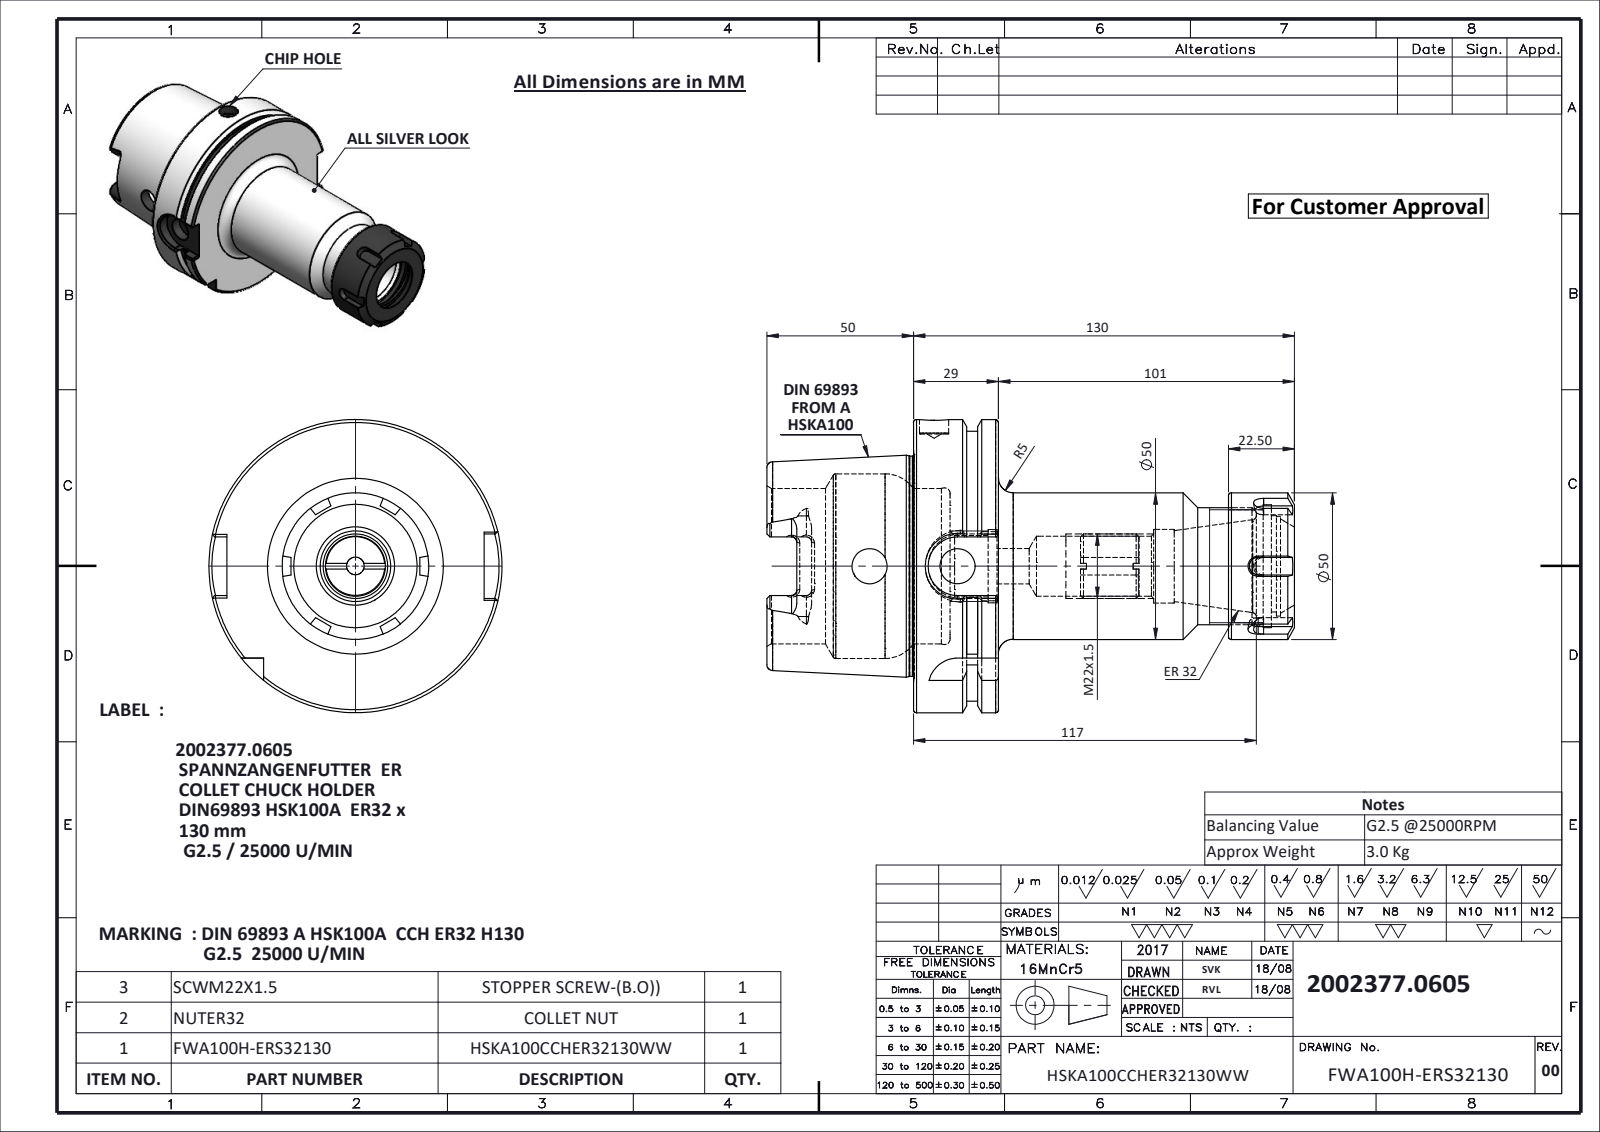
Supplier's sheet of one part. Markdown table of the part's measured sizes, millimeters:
| quantity | value |
| --- | --- |
| part name | FTNUTER32; FWA100H-ERS32130; FTSCWM22X1.5; HSKA100CCHER32130WW |
| STEP written by | SolidWorks 2024 (CONFIG_CONTROL_DESIGN) |
| units | millimeters |
| bodies | 3 solids, 259 faces (95 planar, 68 cylindrical, 96 other) |
| overall size | 180 × 100 × 100 |
| volume | 400 934 mm³ |
| surface area | 79 526 mm² |
| round holes (diameter × count) | 12 × 3, 6 × 1, 10 × 1, 20.5 × 1, 21 × 1, 25 × 1, 25.2 × 1, 32.8 × 1, 34 × 1, 38.5 × 1, 42 × 1, 53 × 1 |
| round bosses / shafts (diameter × count) | 100 × 1, 92 × 1, 75.16 × 1, 50 × 1, 40 × 1, 22 × 1 |
| partial cylindrical surfaces (radius × count) | 1.8 × 6, 4.88 × 4, 10 × 2, 11 × 1 |
| main face-to-face distances | 29, 12.5, 16.5, 79, 78.5, 50, 62.5, 180, 130, 117.5 |
| hole center spacings | 1.6, 30 |
